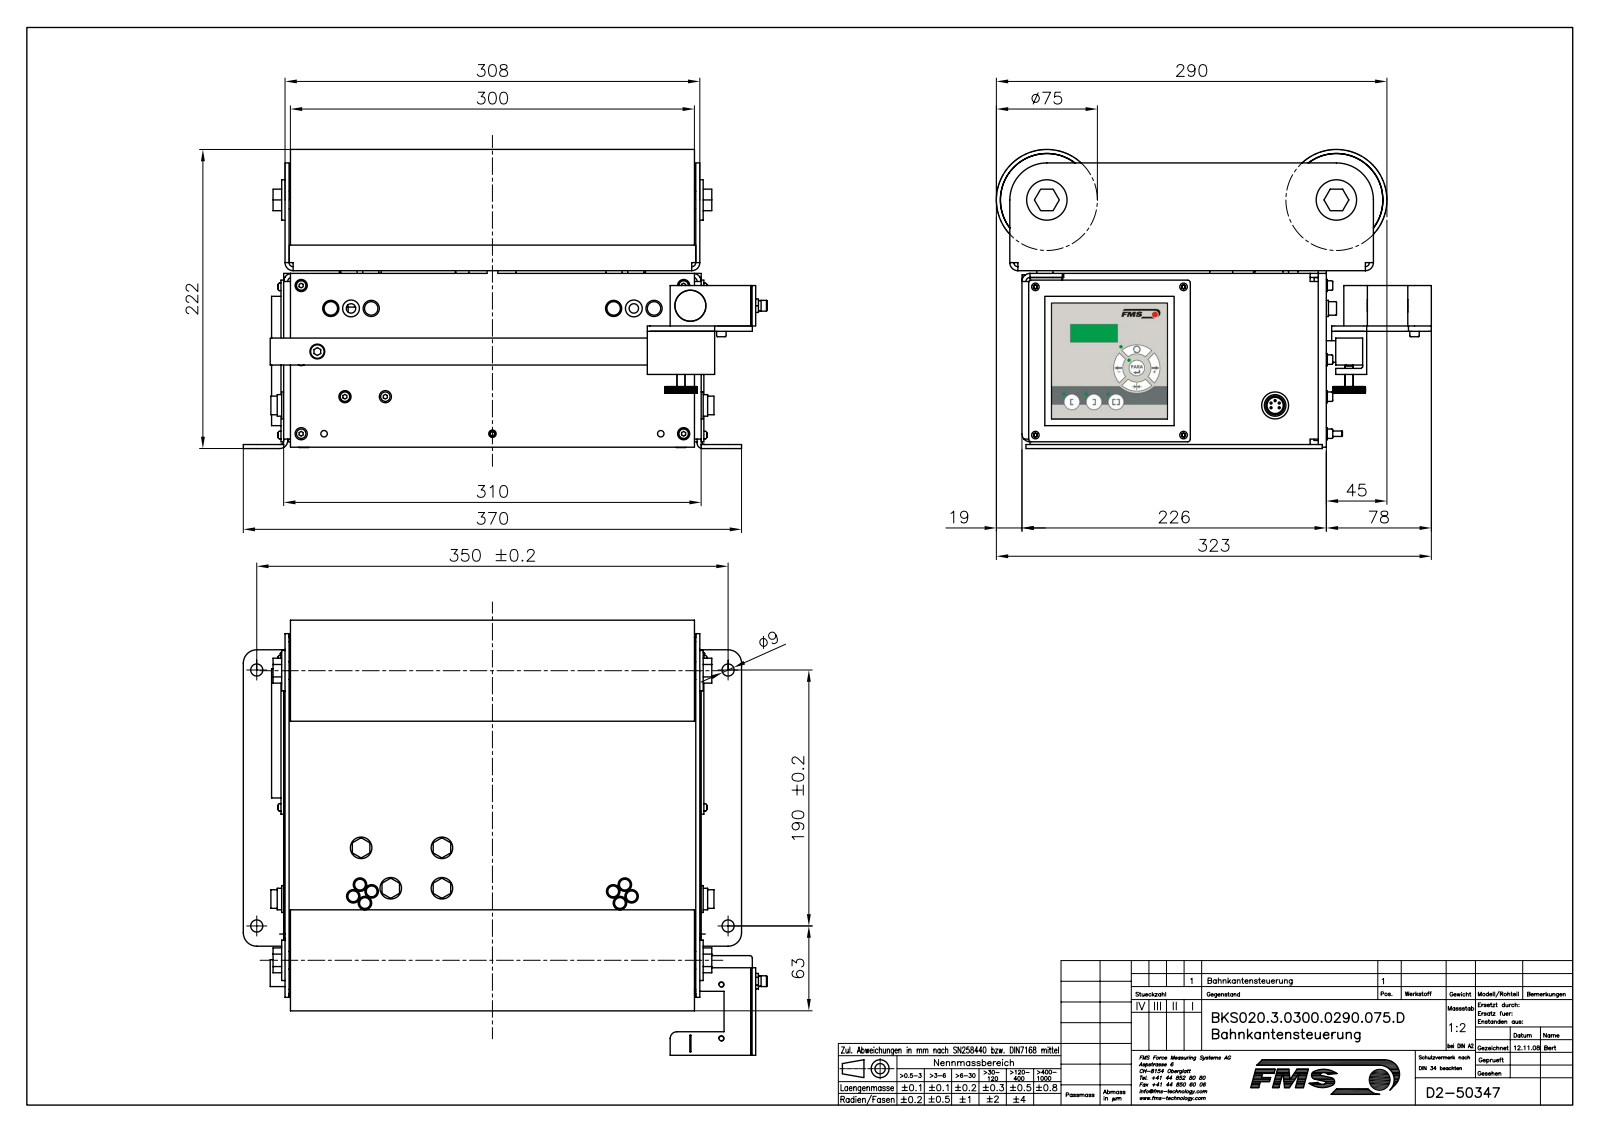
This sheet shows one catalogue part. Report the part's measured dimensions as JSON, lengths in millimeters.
{"part_name": "K50347; K49778; K49776; TEIL1 (+8 more)", "step_written_by": "Mechanical Desktop 2007 (CONFIG_CONTROL_DESIGN)", "units": "millimeters", "bodies": {"solids": 157, "faces": 5792, "planar": 3581, "cylindrical": 1771, "other": 440}, "overall_size": [389.1, 323, 222], "volume_mm3": 2449000, "surface_area_mm2": 1452000, "round_holes": [[3, 30], [4.3, 14], [3.42, 13], [2.2, 8], [2.6, 8], [3.2, 8], [5.3, 8], [6.4, 8], [3.5, 7], [6, 6], [8.4, 6], [1, 4]], "round_bosses_or_shafts": [[10, 18], [4, 18], [8, 15], [6, 11], [7, 10], [12, 8], [9, 8], [5, 8]], "partial_cylinders_radius": [[0.32, 48], [1, 29], [0.25, 24], [2, 24], [0.2, 20], [0.25, 19], [3, 14], [6, 13]], "face_to_face_distances": [3, 1, 2, 127, 5, 4, 130, 6, 306, 128], "hole_center_spacings": [10, 83.5, 97.44, 97.87, 110, 15, 30, 198.06]}
